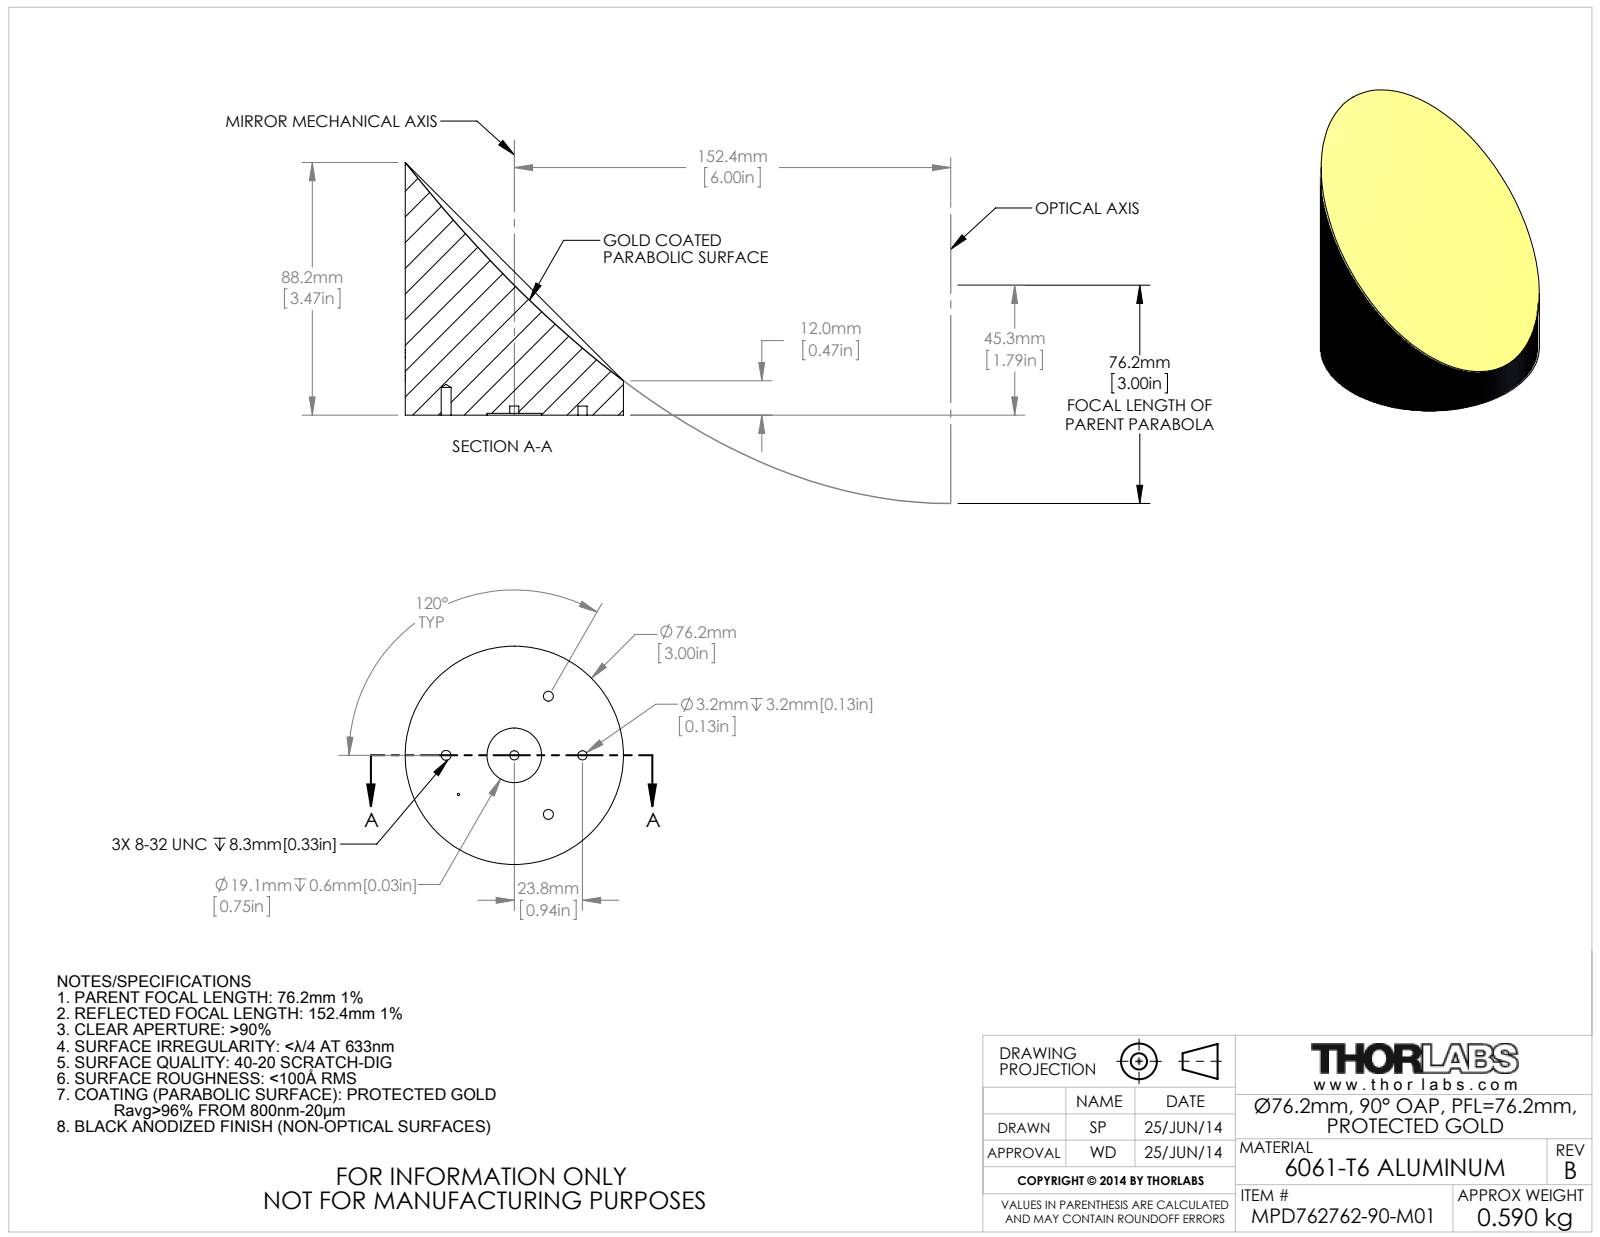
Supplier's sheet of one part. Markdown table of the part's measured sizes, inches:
| quantity | value |
| --- | --- |
| part name | 24805-E0W |
| STEP written by | SolidWorks 2014 (CONFIG_CONTROL_DESIGN) |
| units | inches |
| bodies | 1 solid, 64 faces (4 planar, 50 cylindrical, 10 other) |
| overall size | 3.473 × 3 × 3 |
| volume | 13.25 in³ |
| surface area | 36.36 in² |
| round holes (diameter × count) | 0.136 × 3, 0.126 × 2, 0.75 × 1 |
| round bosses / shafts (diameter × count) | 3 × 1 |
| main face-to-face distances | 0.025, 0.125, 0.1 |
| hole center spacings | 0.937, 0.938, 1.624, 1.624, 1.875 |
